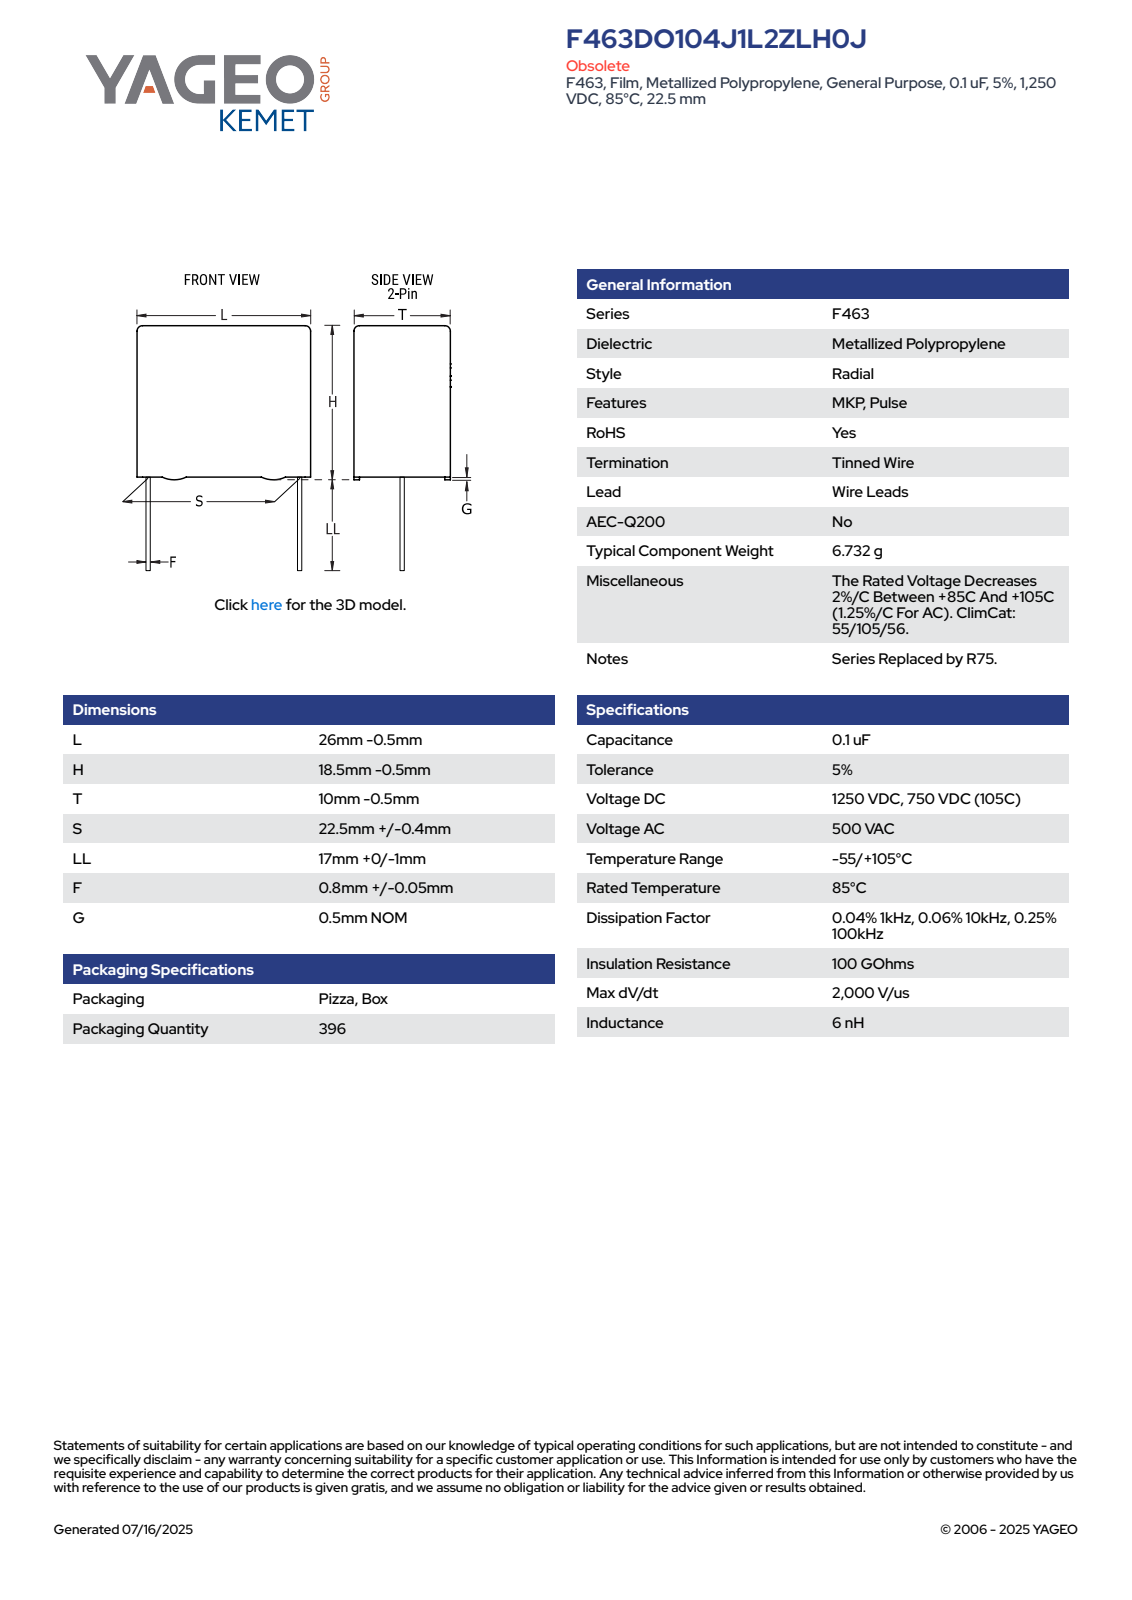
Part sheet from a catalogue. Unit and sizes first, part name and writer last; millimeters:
Units: millimetres
Overall size (bounding box): 35 × 25.5 × 9.51
Round bosses / shafts (diameter × count): ⌀0.85 ×2
Partial cylindrical surfaces — rounded edges, fillets, slot ends (radius × count): R0.5 ×4
Main face-to-face distances: 9.5, 17.5, 25.5, 0.5, 18, 0.54, 8.96, 8.42, 17, 35
Volume: 4 260 mm³ · Surface area: 1 876 mm²
Bodies: 4 solids, 89 faces (81 planar, 8 cylindrical, 0 other)
Part name (STEP PRODUCT): CFR_RBG_26X18.5X10_L25.5H18T9.5S22.5LL17F0.85G0.5
STEP written by: SolidWorks 2014 (AUTOMOTIVE_DESIGN)
